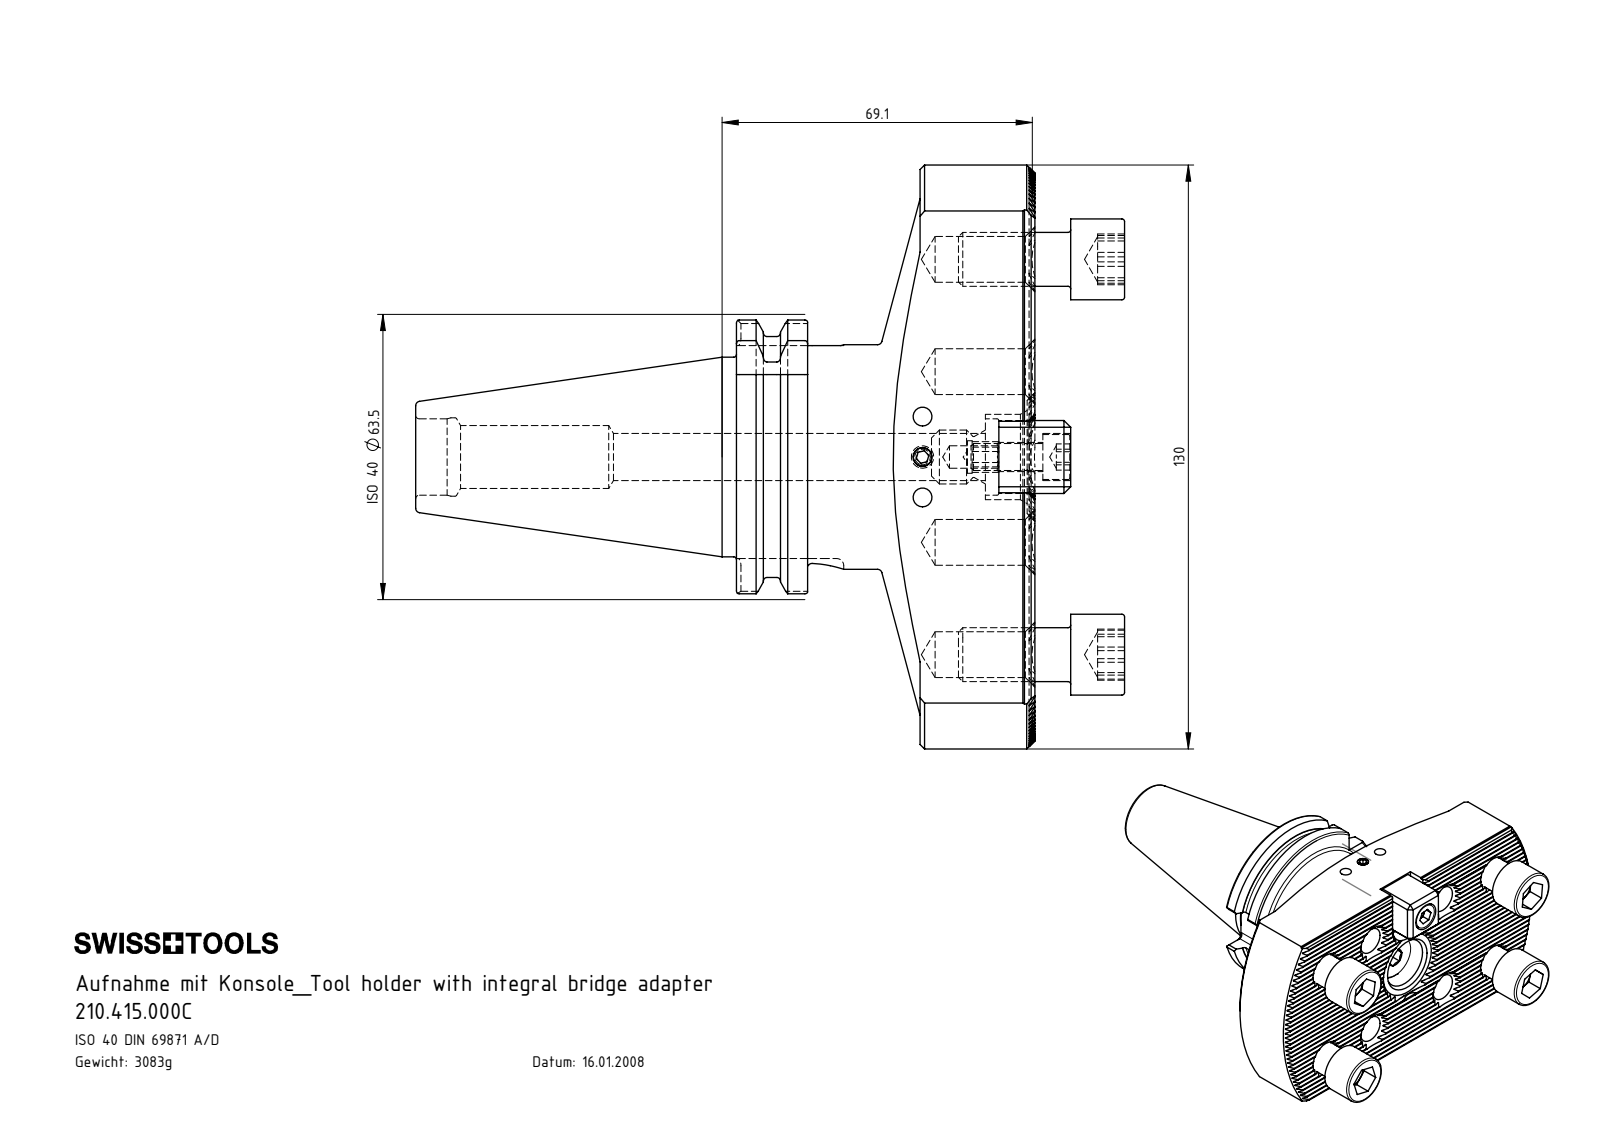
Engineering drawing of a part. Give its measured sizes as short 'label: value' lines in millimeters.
name: 210.415.000C; Ko1-ER1.001.016_A; ISO 4762 M6 x 16; ISO 4762 M12 x 25 (+3 more)
written by: SolidWorks 2017 (CONFIG_CONTROL_DESIGN)
unit: mm
bodies: 10 solids, 886 faces (502 planar, 210 cylindrical, 174 other)
size: 157.9 × 130 × 70
volume: 392 696 mm³; area: 72 489 mm²
holes: 8× ⌀10.2, 3× ⌀4.2, 2× ⌀10.5, 1× ⌀5, 1× ⌀6.5, 1× ⌀7.24, 1× ⌀14, 1× ⌀17, 1× ⌀17.45, 1× ⌀19
bosses: 5× ⌀12, 4× ⌀18, 1× ⌀50, 1× ⌀44.45, 1× ⌀10, 1× ⌀6, 1× ⌀5
rounds: 34× R0.14, 8× R1.6, 1× R7.95, 1× R8, 1× R8.05, 1× R28, 1× R31.75, 1× R65
face distances: 1.73, 17.32, 70, 8.66, 3.46, 5.2, 6.93, 15.59, 19.05, 3.47
hole spacings: 25, 27.59, 40, 47.17, 48.33, 63, 74.63, 9
